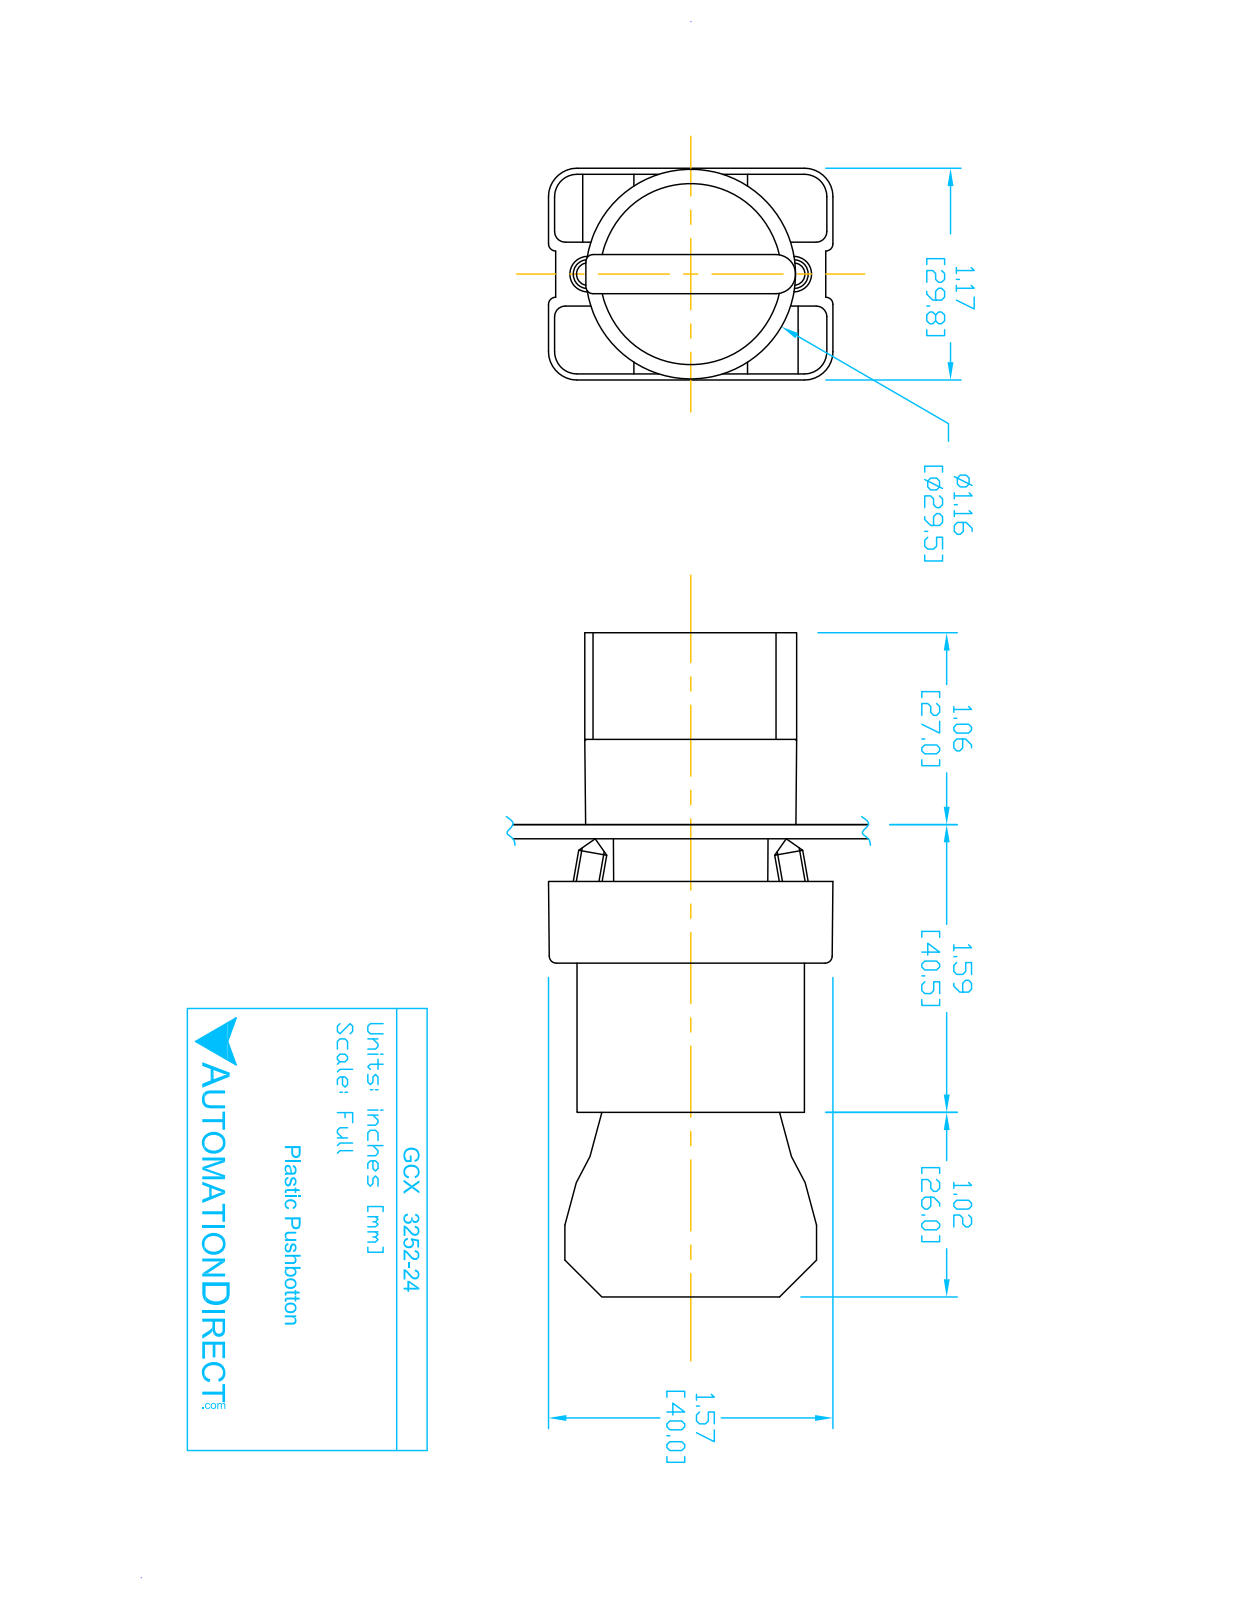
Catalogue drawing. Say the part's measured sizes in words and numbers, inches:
The part is named "ECX1050; GCX3252-24; ecx1040; ECX3029-2 (+1 more)". Its 3-D file was written by "SolidWorks 2016 (AUTOMOTIVE_DESIGN)". It is 8 solids with 445 faces: 263 planar, 151 cylindrical and 31 other. Overall it measures 3.653 by 1.581 by 1.177 inches. Its volume is 2.799 cubic inches and its surface area 39 square inches. Round holes: 2 of diameter 0.079, 2 of diameter 0.124, 2 of diameter 0.13, 1 of diameter 0.087, 1 of diameter 0.197, 1 of diameter 0.469, 1 of diameter 0.878, 1 of diameter 0.888, 1 of diameter 1.024. Round bosses or shafts: 4 of diameter 0.157, 1 of diameter 1.175, 1 of diameter 1.004, 1 of diameter 0.945, 1 of diameter 0.856, 1 of diameter 0.78, 1 of diameter 0.504. Partial cylindrical surfaces (rounded edges, fillets, slot ends): 24 of radius 0.059, 12 of radius 0.041, 12 of radius 0.124, 12 of radius 0.157, 9 of radius 0.039, 2 of radius 0.128, 1 of radius 0.02, 1 of radius 0.063. The main face-to-face distances are 0.827, 2.02, 1.193, 0.579, 1.244, 1.171, 0.472, 0.469, 0.031, 0.033. The hole center spacings are 0.236, 0.544, 0.472, 0.49.
